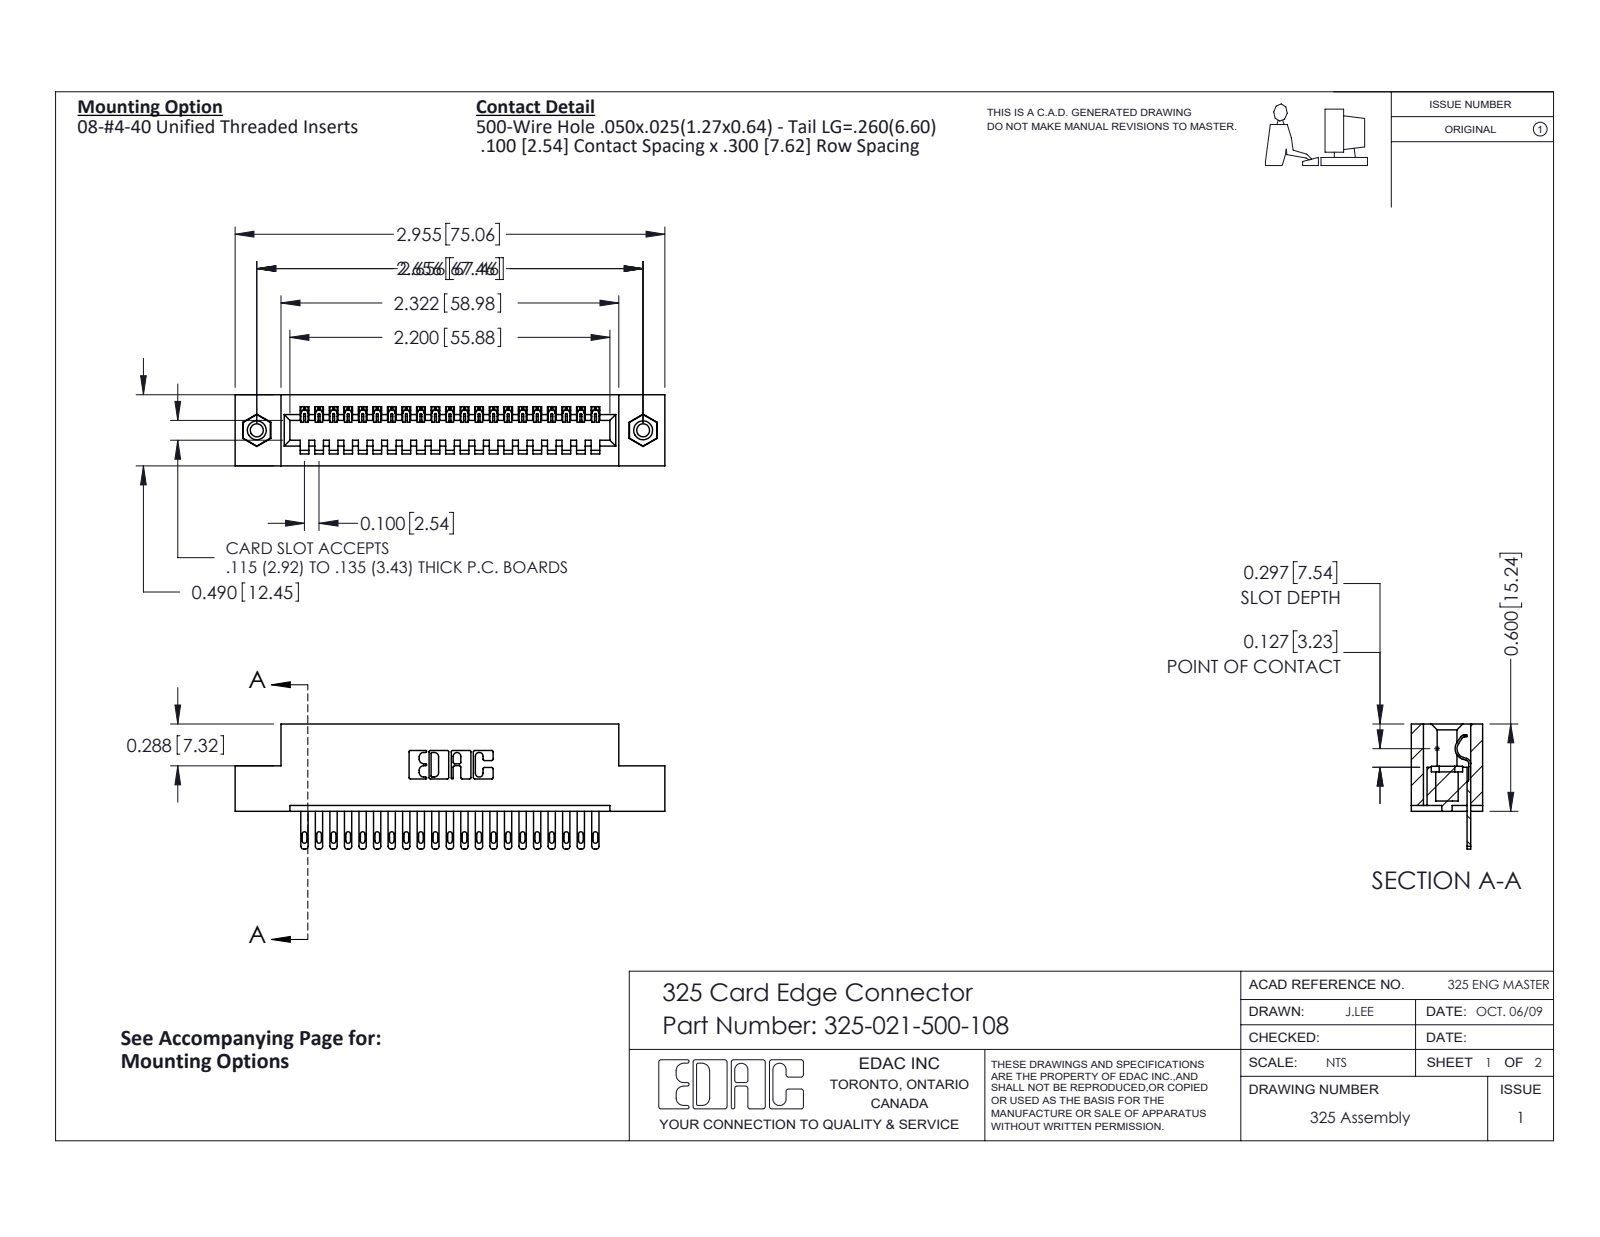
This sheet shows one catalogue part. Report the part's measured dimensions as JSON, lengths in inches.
{"part_name": "325-292-001_325-293-100; 325-021-500-108; 325 Part_TI; 345-250-001_345-250-003-102", "step_written_by": "SolidWorks 2016 (CONFIG_CONTROL_DESIGN)", "units": "inches", "bodies": {"solids": 24, "faces": 1308, "planar": 858, "cylindrical": 434, "other": 16}, "overall_size": [2.955, 0.86, 0.49], "volume_in3": 0.572, "surface_area_in2": 15.41, "round_holes": [[0.089, 2], [0.125, 2], [0.16, 2]], "round_bosses_or_shafts": [[0.155, 2]], "partial_cylinders_radius": [[0.006, 42], [0.016, 42], [0.02, 42], [0.01, 22], [0.007, 6], [0.031, 6], [0.026, 3], [0.014, 1]], "face_to_face_distances": [0.083, 0.407, 0.3, 0.49, 0.107, 0.383, 0.025, 0.6, 0.04, 0.1], "hole_center_spacings": [2.656]}
